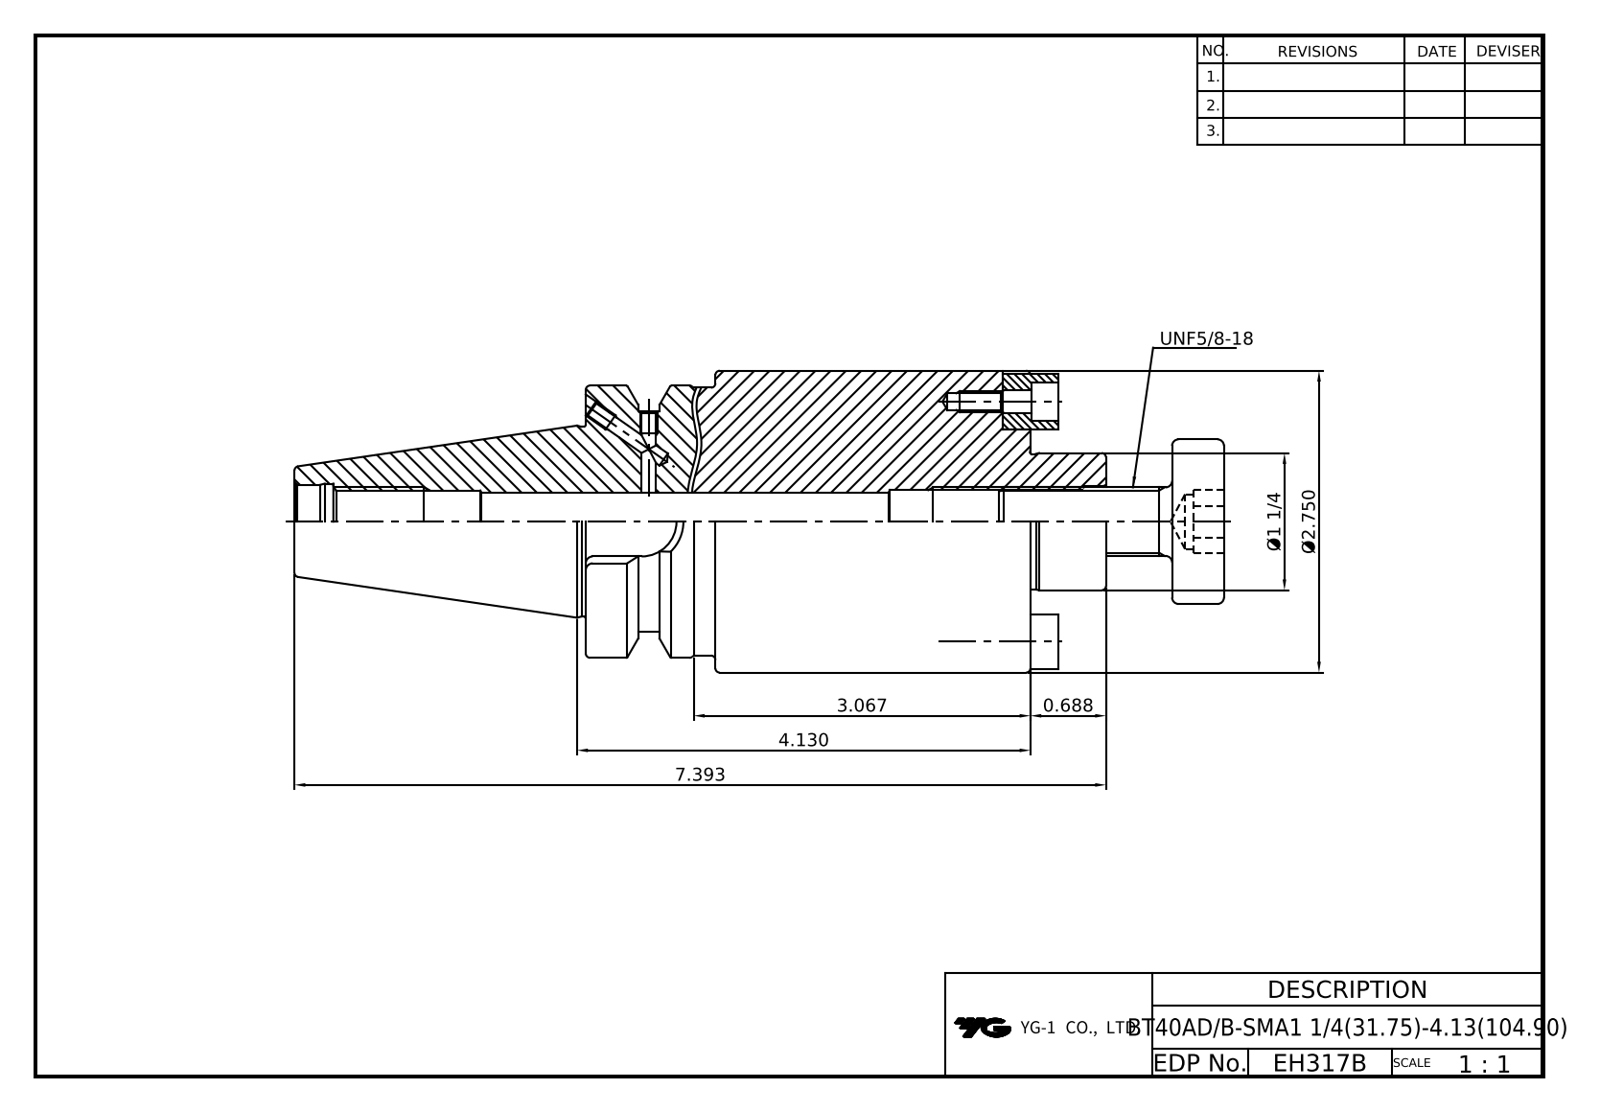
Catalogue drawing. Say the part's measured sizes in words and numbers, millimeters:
The part is named "LO-BT40ADB-SMA31.75-104.9; DRIVE KEY-12.7x12.7x12.7; HEX'' WRENCH BOLT-UNC#10-24x1_2L; COLLAR BOLT-UNF5_8-18x40L". Its 3-D file was written by "Autodesk Inventor 2025 (AP242_MANAGED_MODEL_BASED_3D_ENGINEERING_MIM_LF)". It is 6 solids with 148 faces: 72 planar, 45 cylindrical and 31 other. Overall it measures 209.8 by 69.9 by 69.9 millimeters. Its volume is 432 900 cubic millimeters and its surface area 57 460 square millimeters. Round holes: 4 of diameter 3.3, 4 of diameter 4, 2 of diameter 3.7, 2 of diameter 5.5, 2 of diameter 8.7, 1 of diameter 12.7, 1 of diameter 13.8, 1 of diameter 14.4, 1 of diameter 16.5, 1 of diameter 17, 1 of diameter 17.6. Round bosses or shafts: 2 of diameter 7.9, 2 of diameter 4.8, 1 of diameter 69.9, 1 of diameter 63, 1 of diameter 62, 1 of diameter 52.6, 1 of diameter 44, 1 of diameter 38.1. Partial cylindrical surfaces (rounded edges, fillets, slot ends): 2 of radius 6.4, 1 of radius 8.1. The main face-to-face distances are 102.9, 30, 142.4, 39.5, 72.9, 112.4, 130.4, 100.4, 27.5, 12. The hole center spacings are 27.8, 27.8, 55.5, 55.5, 55.5.
